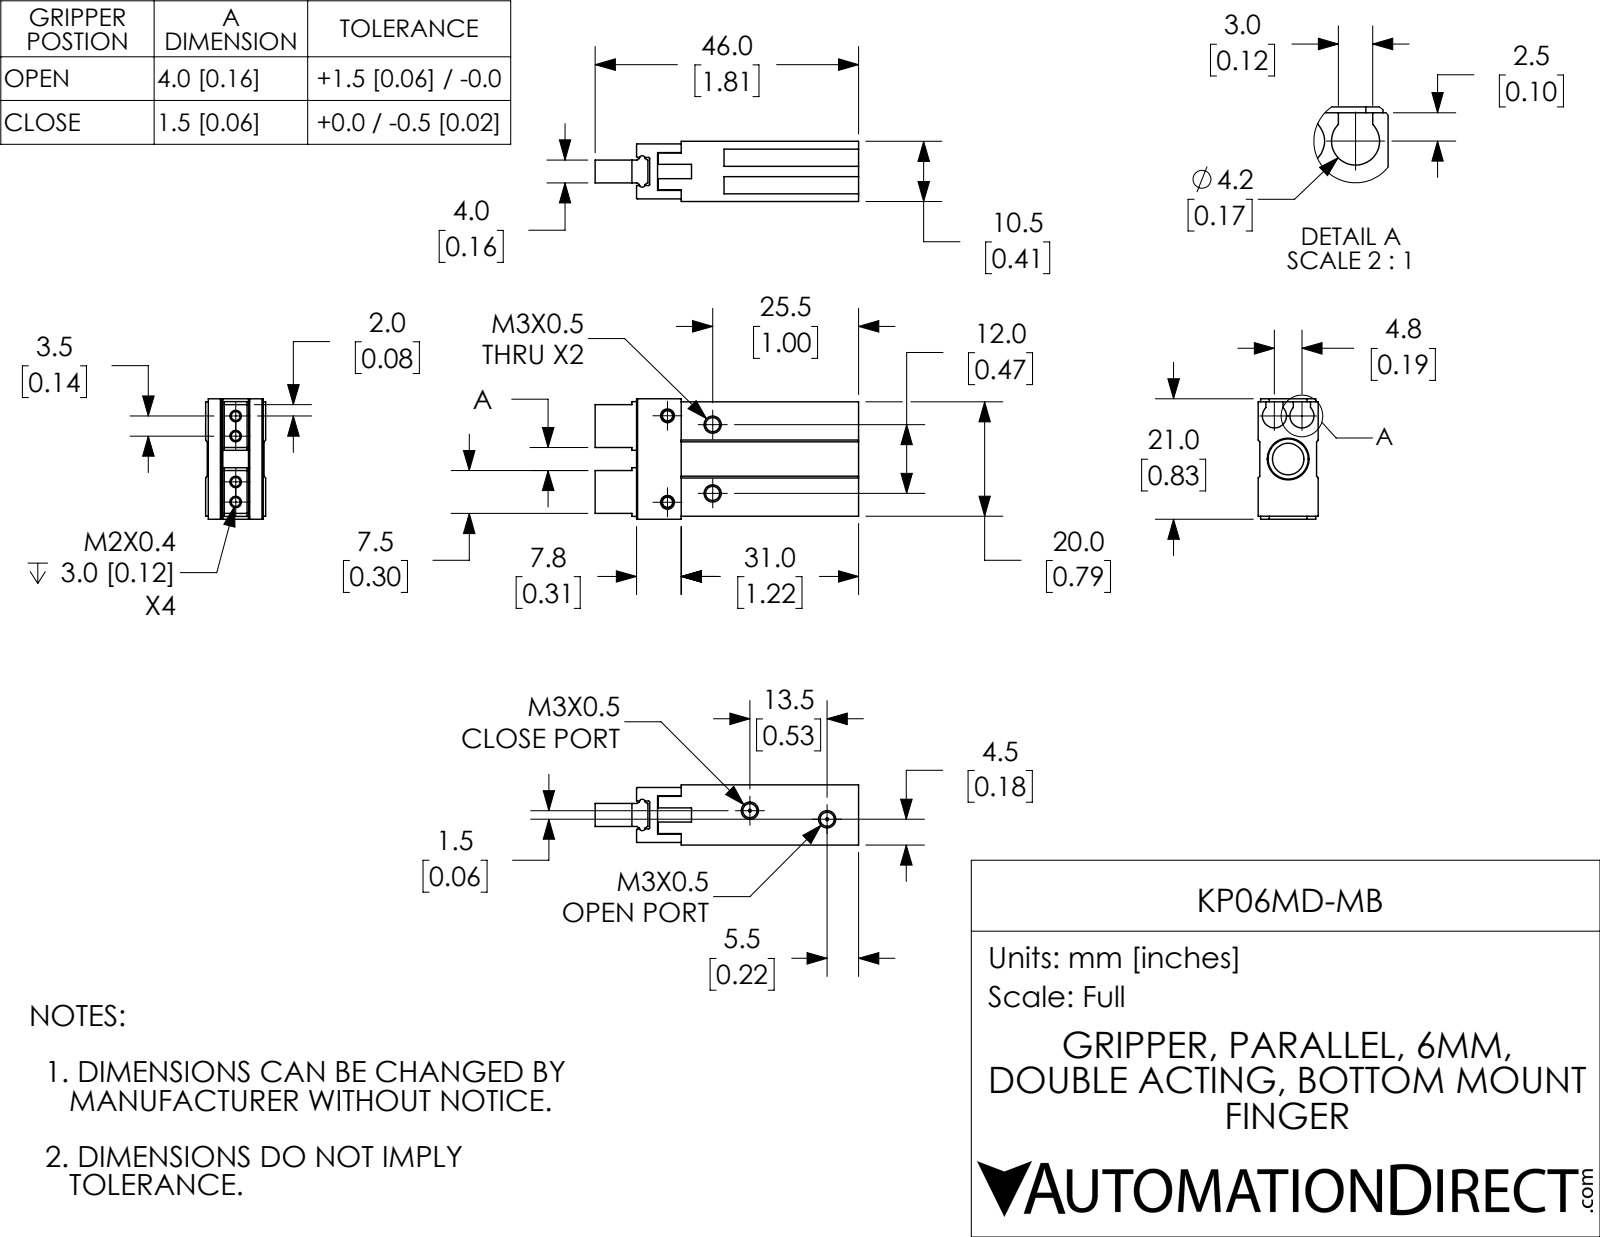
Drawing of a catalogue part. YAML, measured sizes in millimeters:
part_name: "KP06MD-MB; KP06MD-MB-1; KP06MD-MB-2; KP06MD-MB-3"
step_written_by: "SolidWorks 2017 (CONFIG_CONTROL_DESIGN)"
units: millimeters
bodies: {solids: 3, faces: 180, planar: 98, cylindrical: 44, other: 38}
overall_size: [46, 21, 10.5]
volume: 6981
surface_area: 5051
round_holes:
  - {diameter: 2.46, count: 3}
  - {diameter: 0.5, count: 2}
  - {diameter: 1.57, count: 2}
  - {diameter: 1.57, count: 2}
  - {diameter: 3.1, count: 2}
  - {diameter: 2.46, count: 1}
  - {diameter: 5.5, count: 1}
  - {diameter: 7, count: 1}
partial_cylinders:
  - {radius: 0.2, count: 4}
  - {radius: 0.5, count: 2}
  - {radius: 2.1, count: 2}
face_to_face_distances: [3.25, 4, 10.5, 2, 3.7, 10.2, 0.45, 6.5, 10.05, 9.75]
hole_center_spacings: [3.5, 4, 7.5, 11.5, 8, 12, 13.58, 15]
